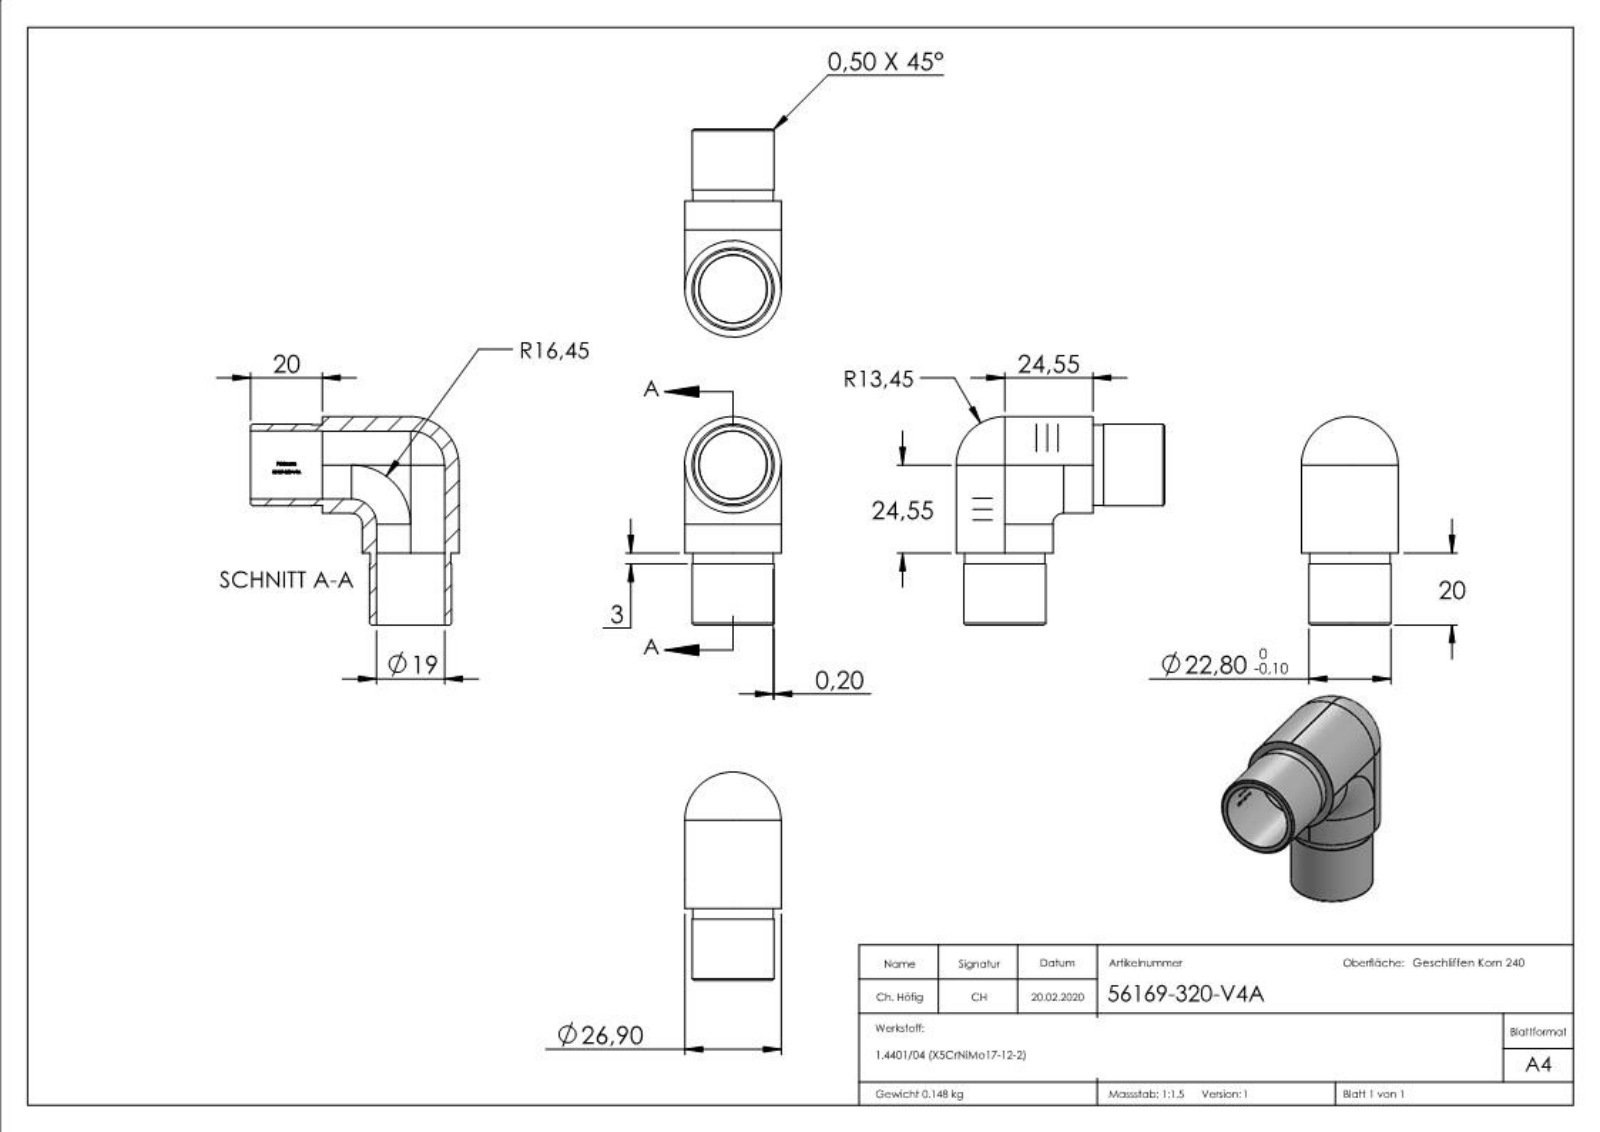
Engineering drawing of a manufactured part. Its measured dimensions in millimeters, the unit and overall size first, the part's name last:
Units: millimetres
Overall size (bounding box): 58 × 58 × 26.9
Round holes (diameter × count): ⌀18.9 ×2, ⌀19 ×2
Round bosses / shafts (diameter × count): ⌀26.9 ×2, ⌀22.8 ×2, ⌀22.4 ×2
Partial cylindrical surfaces — rounded edges, fillets, slot ends (radius × count): R9.6 ×1
Main face-to-face distances: 20, 4, 22.9, 18.9, 26.9, 17, 3, 1.06, 0.99, 2.77
Volume: 18 465 mm³ · Surface area: 12 631 mm²
Bodies: 1 solid, 309 faces (135 planar, 52 cylindrical, 122 other)
Part name (STEP PRODUCT): 56169-320-V4A
STEP written by: SolidWorks 2015 (CONFIG_CONTROL_DESIGN)
